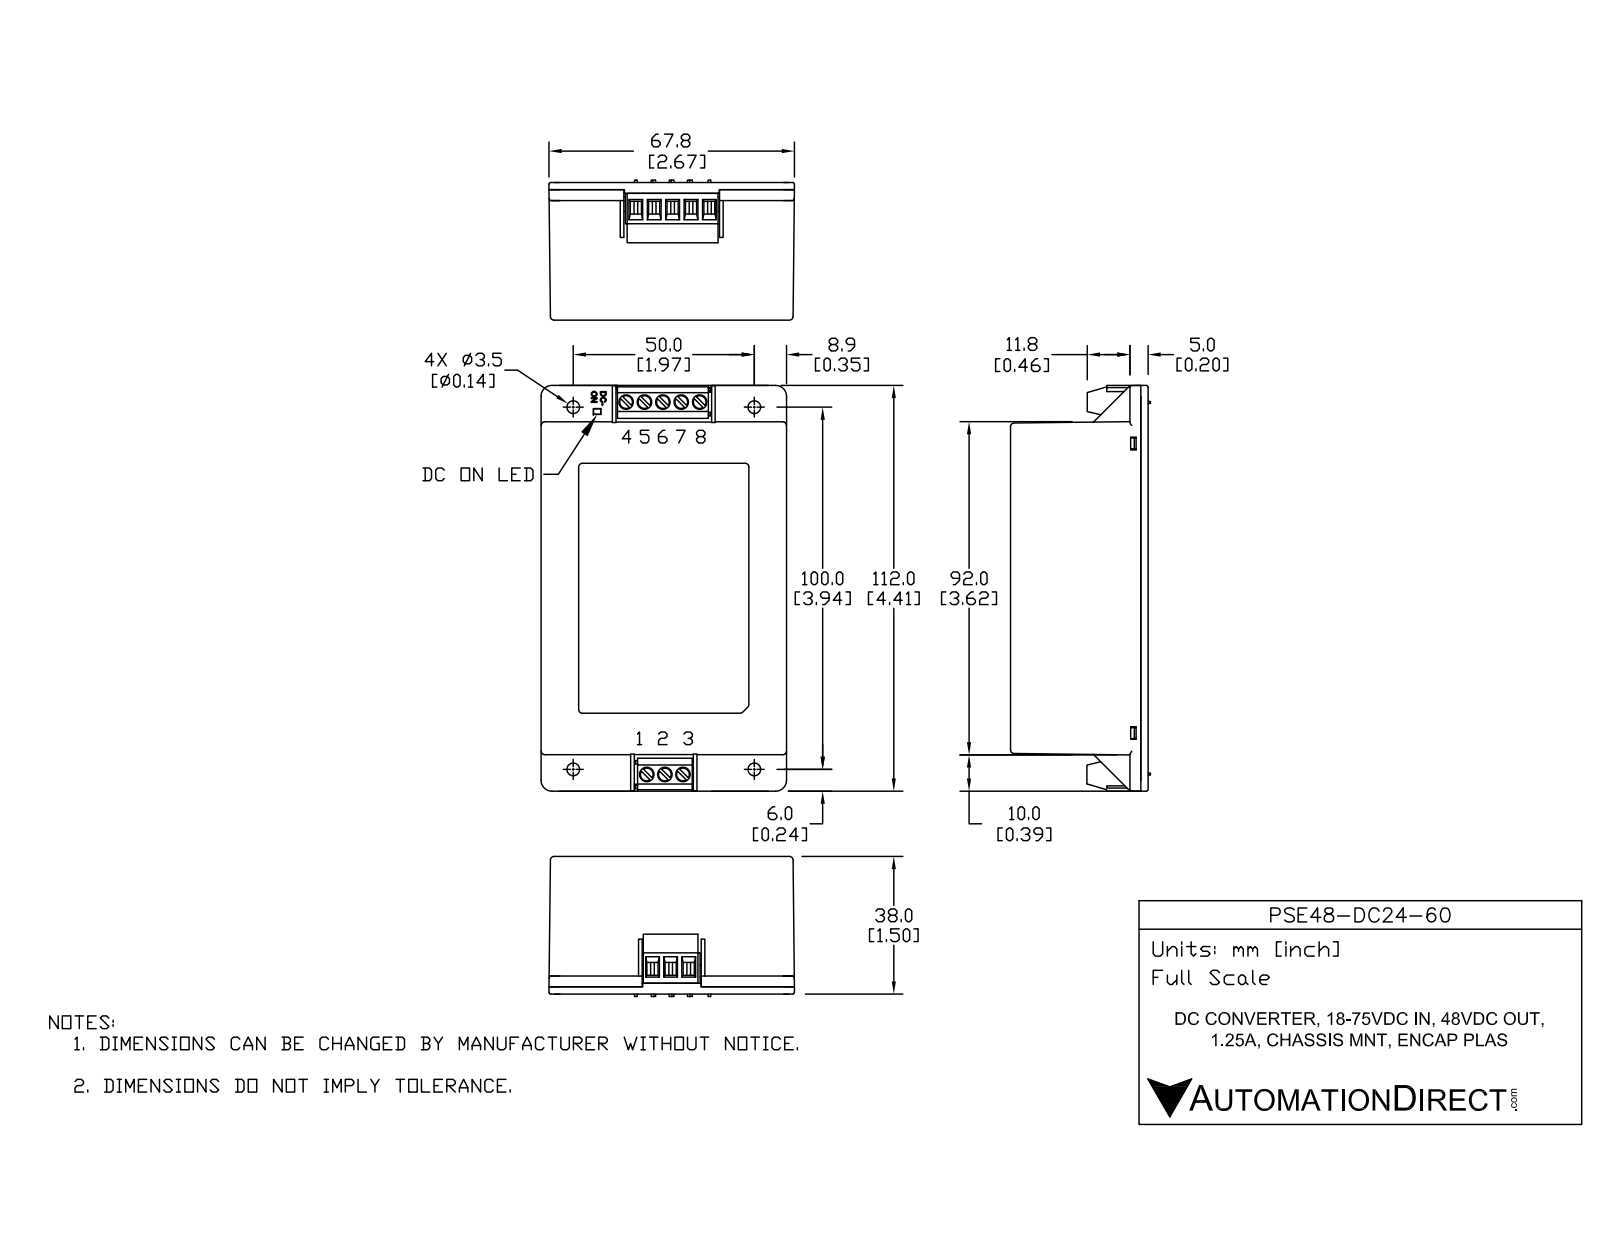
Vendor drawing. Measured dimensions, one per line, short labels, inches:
name: PSE48-DC24-60
written by: SolidWorks 2015 (AUTOMOTIVE_DESIGN)
unit: in
bodies: 0 solids, 390 faces (282 planar, 89 cylindrical, 19 other)
size: 4.446 × 2.728 × 1.459
holes: 10× ⌀0.157, 4× ⌀0.138, 1× ⌀0.097, 1× ⌀0.161, 1× ⌀0.256
bosses: 4× ⌀0.059, 1× ⌀0.197
rounds: 17× R0.039, 8× R0.02, 4× R0.085, 4× R0.104, 4× R0.118, 3× R0.128
face distances: 0.039, 0.039, 1.378, 1.339, 0.028, 0.04, 0.067, 1.311, 1.378, 1.338
hole spacings: 0.2, 0.4, 1.969, 4.021, 4.027, 0.197, 0.6, 3.937
